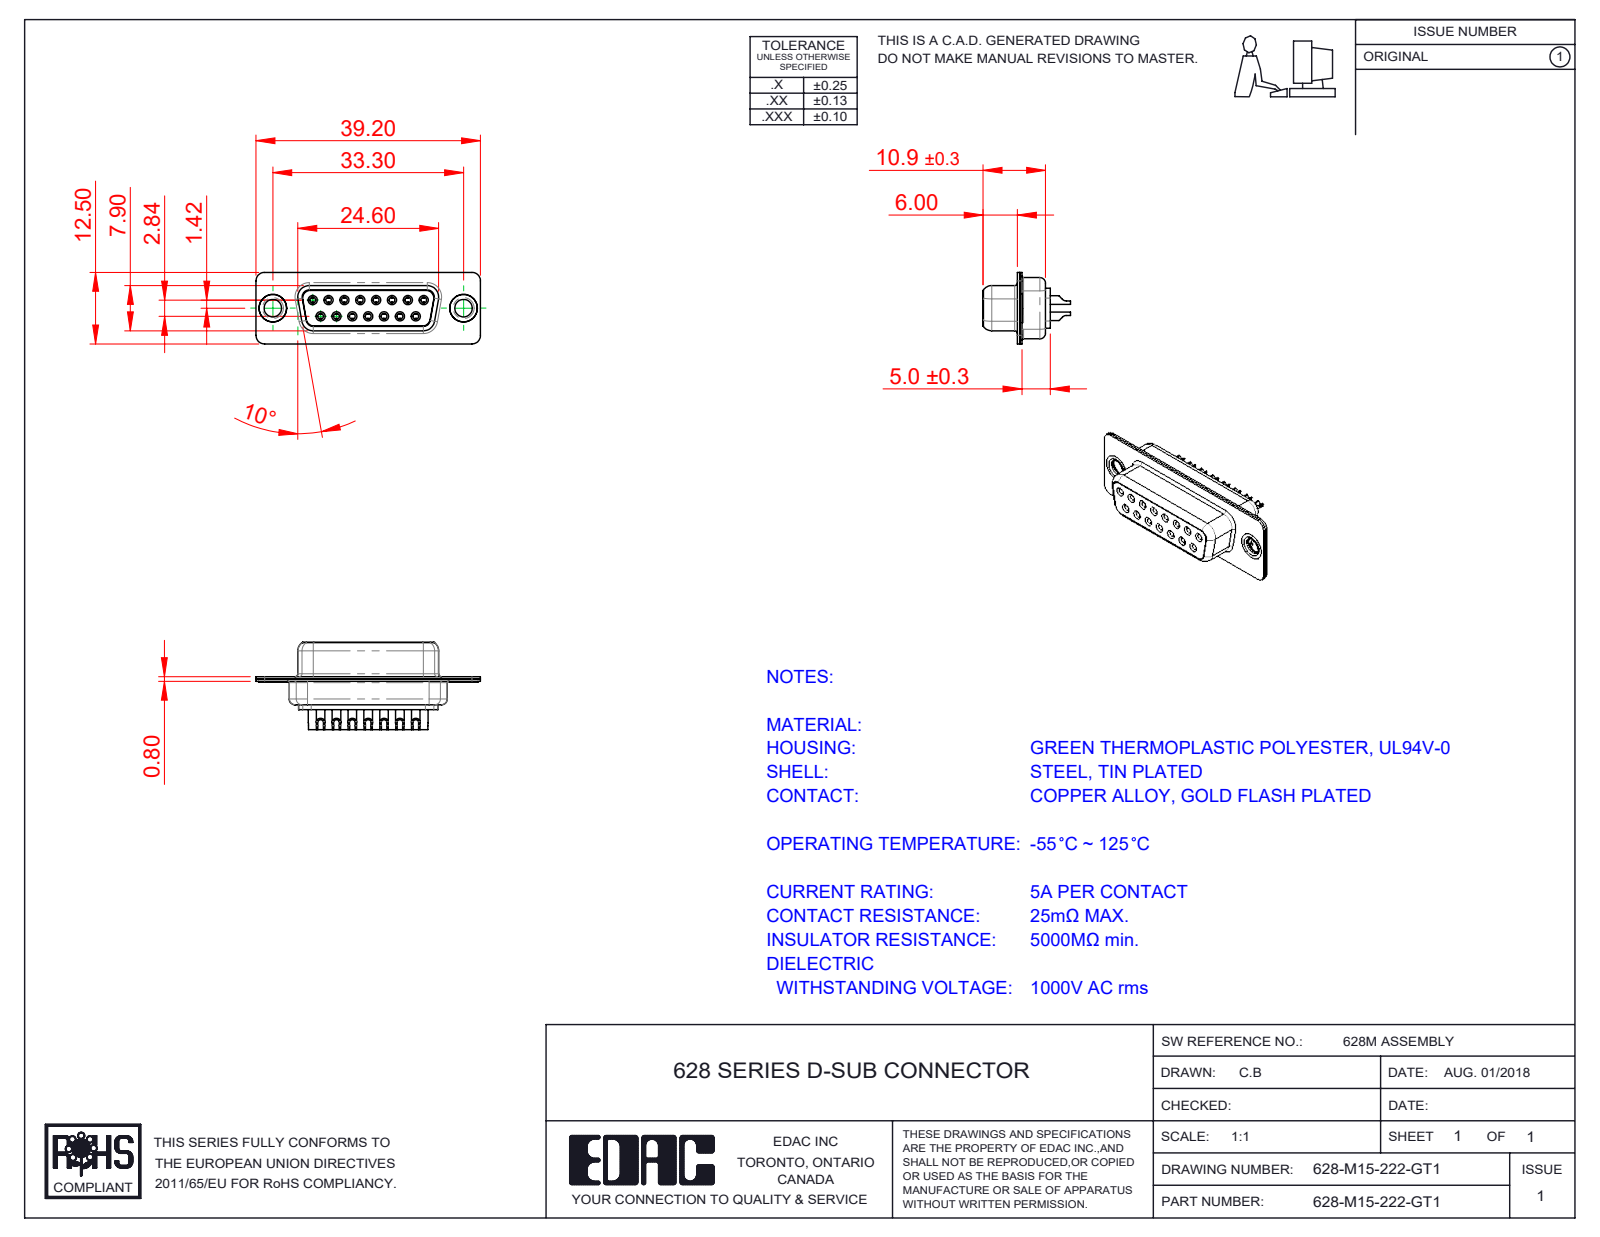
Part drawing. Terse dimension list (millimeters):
name: 628M Shell Front_15 Contacts; 628-M15-222-GT1; 628M Thru Hole Rivet; 628M Shell Rear_15 Contacts (+3 more)
written by: SolidWorks 2020 (CONFIG_CONTROL_DESIGN)
unit: mm
bodies: 20 solids, 1079 faces (323 planar, 436 cylindrical, 320 other)
size: 39.2 × 15.25 × 12.5
volume: 2 415 mm³; area: 6 179 mm²
holes: 15× ⌀1, 15× ⌀1.1, 15× ⌀1.7, 15× ⌀1.8, 15× ⌀2, 2× ⌀3.05, 2× ⌀4, 2× ⌀4.8
bosses: 15× ⌀2.2, 15× ⌀1.6, 15× ⌀1.5, 2× ⌀5, 2× ⌀4.9, 2× ⌀3.55
rounds: 16× R1.5, 12× R2, 8× R1.35, 8× R1.6, 6× R1, 4× R0.25, 4× R0.5, 4× R0.6
face distances: 0.4, 1.4, 0.45, 8.45, 8.9, 1.8, 7.05, 0.85, 0.8, 1.85
hole spacings: 3.16, 2.77, 5.54, 8.31, 11.08, 5.03, 5.04, 7.48
